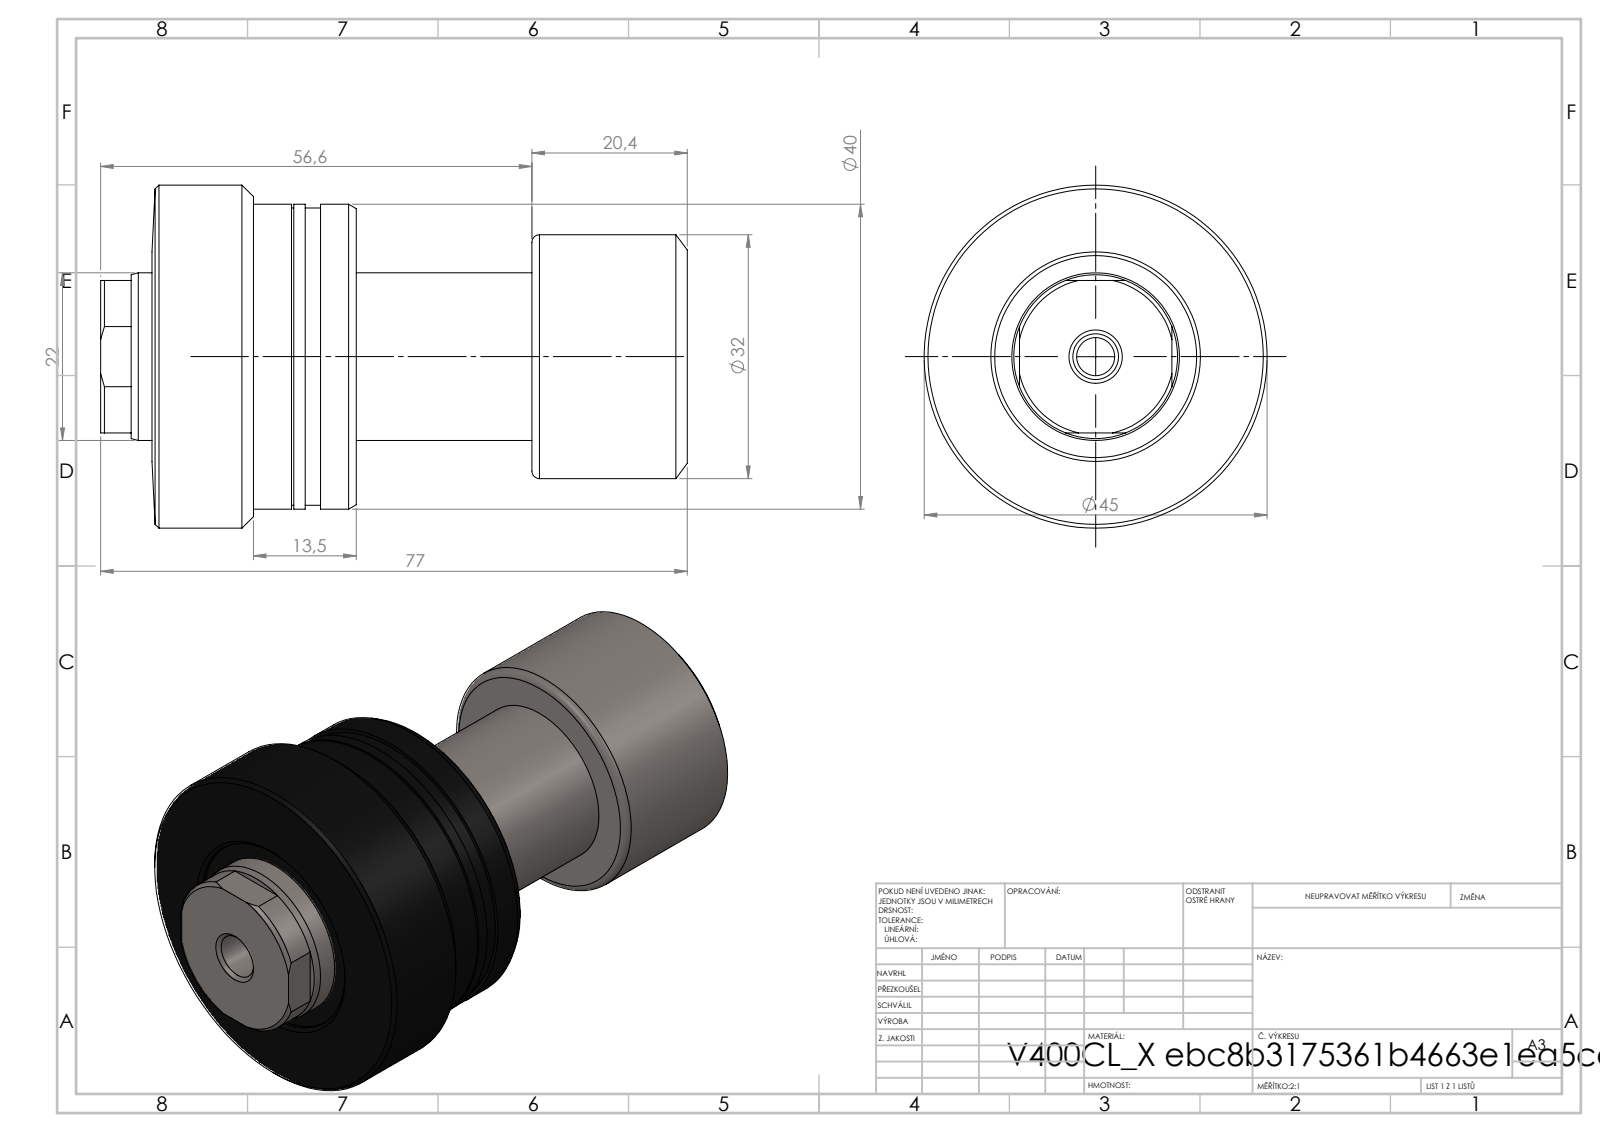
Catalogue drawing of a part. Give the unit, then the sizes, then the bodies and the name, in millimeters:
Units: millimetres
Overall size (bounding box): 77 × 45 × 45
Round holes (diameter × count): ⌀2.05 ×1, ⌀5 ×1, ⌀6 ×1, ⌀22 ×1, ⌀26.5 ×1
Round bosses / shafts (diameter × count): ⌀45 ×1, ⌀40 ×1, ⌀39 ×1, ⌀32 ×1
Partial cylindrical surfaces — rounded edges, fillets, slot ends (radius × count): R10.75 ×1
Main face-to-face distances: 43.45, 20.4, 23.05, 77, 56.6, 33.55, 69.45, 49.05, 26, 7.55
Volume: 64 210 mm³ · Surface area: 15 553 mm²
Bodies: 2 solids, 79 faces (19 planar, 30 cylindrical, 30 other)
Part name (STEP PRODUCT): V400CL_PC_X; V400CL_VC_X
STEP written by: SolidWorks 2019 (CONFIG_CONTROL_DESIGN)
